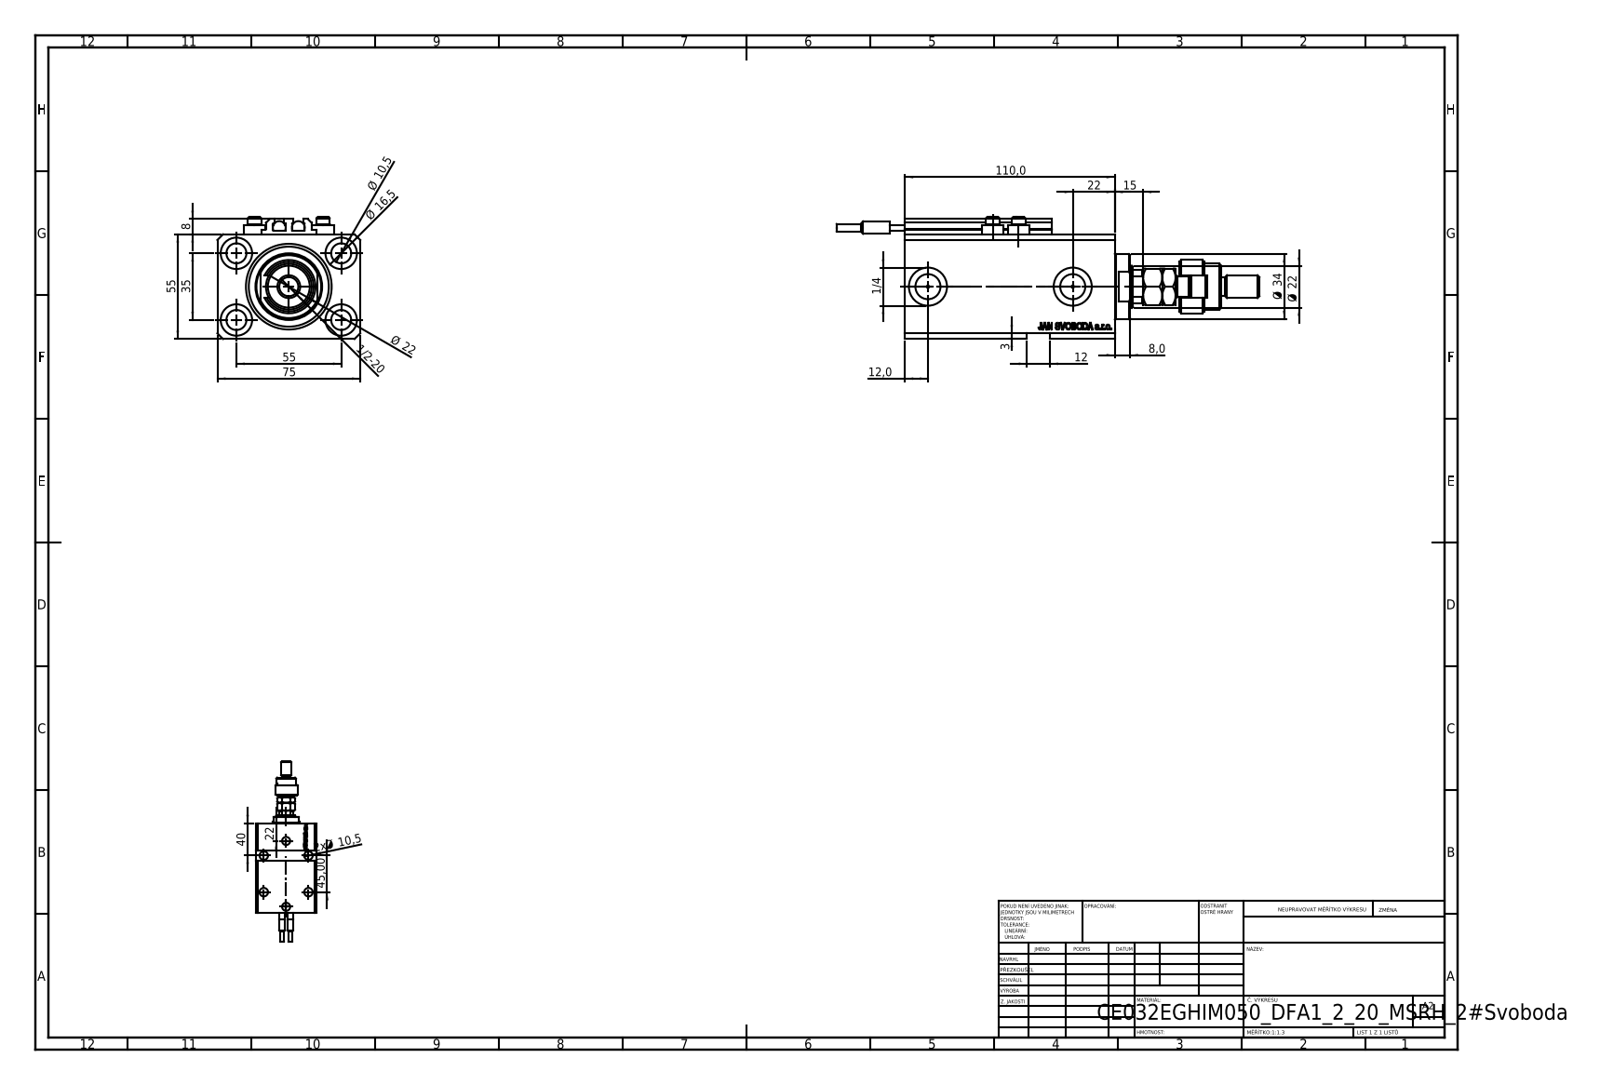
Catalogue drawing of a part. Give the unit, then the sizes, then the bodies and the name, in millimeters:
Units: millimetres
Overall size (bounding box): 222 × 75 × 64
Round holes (diameter × count): ⌀10.5 ×9, ⌀1.25 ×4, ⌀4 ×4, ⌀16.5 ×4, ⌀10 ×2, ⌀13.16 ×2, ⌀20 ×2, ⌀22 ×1, ⌀32 ×1, ⌀45 ×1
Round bosses / shafts (diameter × count): ⌀11.6 ×4, ⌀7 ×4, ⌀6.8 ×2, ⌀6.5 ×2, ⌀4 ×2, ⌀34 ×1, ⌀28 ×1, ⌀24 ×1
Partial cylindrical surfaces — rounded edges, fillets, slot ends (radius × count): R0.2 ×10, R9.75 ×1, R10.5 ×1
Main face-to-face distances: 55, 75, 15, 3, 110, 57, 95, 9.9, 8, 19
Hole centre spacings: 32.6, 32.87, 55, 68.74, 13.6, 14.09, 23.05, 25.81
Volume: 402 791 mm³ · Surface area: 105 514 mm²
Bodies: 12 solids, 1221 faces (574 planar, 171 cylindrical, 476 other)
Part name (STEP PRODUCT): ALLEN BOLT V250CE; SWITCH_V250CE; V250CE_E_Body; V250CE_VC_E (+3 more)
STEP written by: SolidWorks 2019 (CONFIG_CONTROL_DESIGN)
